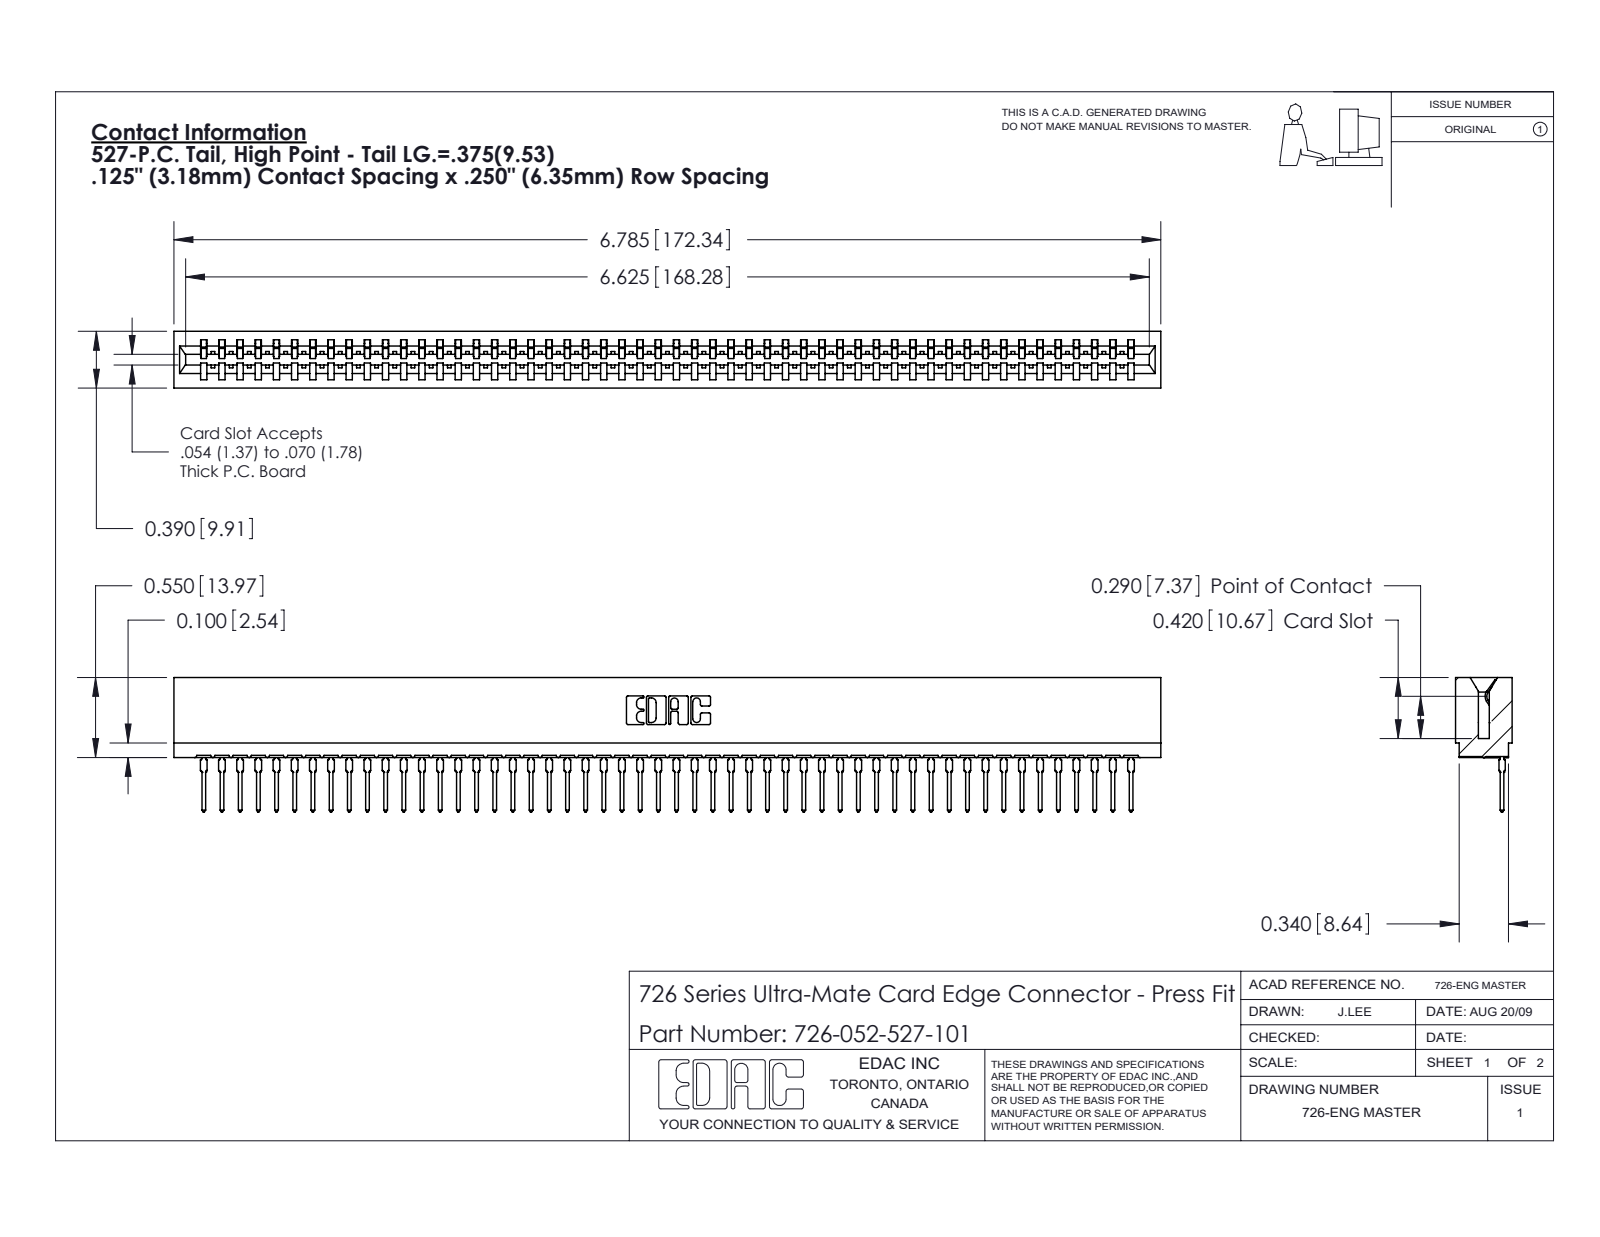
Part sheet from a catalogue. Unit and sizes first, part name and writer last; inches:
Units: inches
Overall size (bounding box): 6.785 × 0.924 × 0.39
Partial cylindrical surfaces — rounded edges, fillets, slot ends (radius × count): R0.021 ×104, R0.015 ×53, R0.01 ×22, R0.007 ×6, R0.031 ×6, R0.005 ×4, R0.011 ×4, R0.026 ×3
Main face-to-face distances: 0.057, 0.333, 0.39, 0.025, 0.307, 0.25, 0.275, 0.083, 0.365, 0.032
Volume: 0.939 in³ · Surface area: 37.07 in²
Bodies: 53 solids, 5713 faces (3331 planar, 1030 cylindrical, 1352 other)
Part name (STEP PRODUCT): 726-052-527-101; 746-292-001_527; 726 Part_.515 Slot Depth - 01
STEP written by: SolidWorks 2020 (CONFIG_CONTROL_DESIGN)
